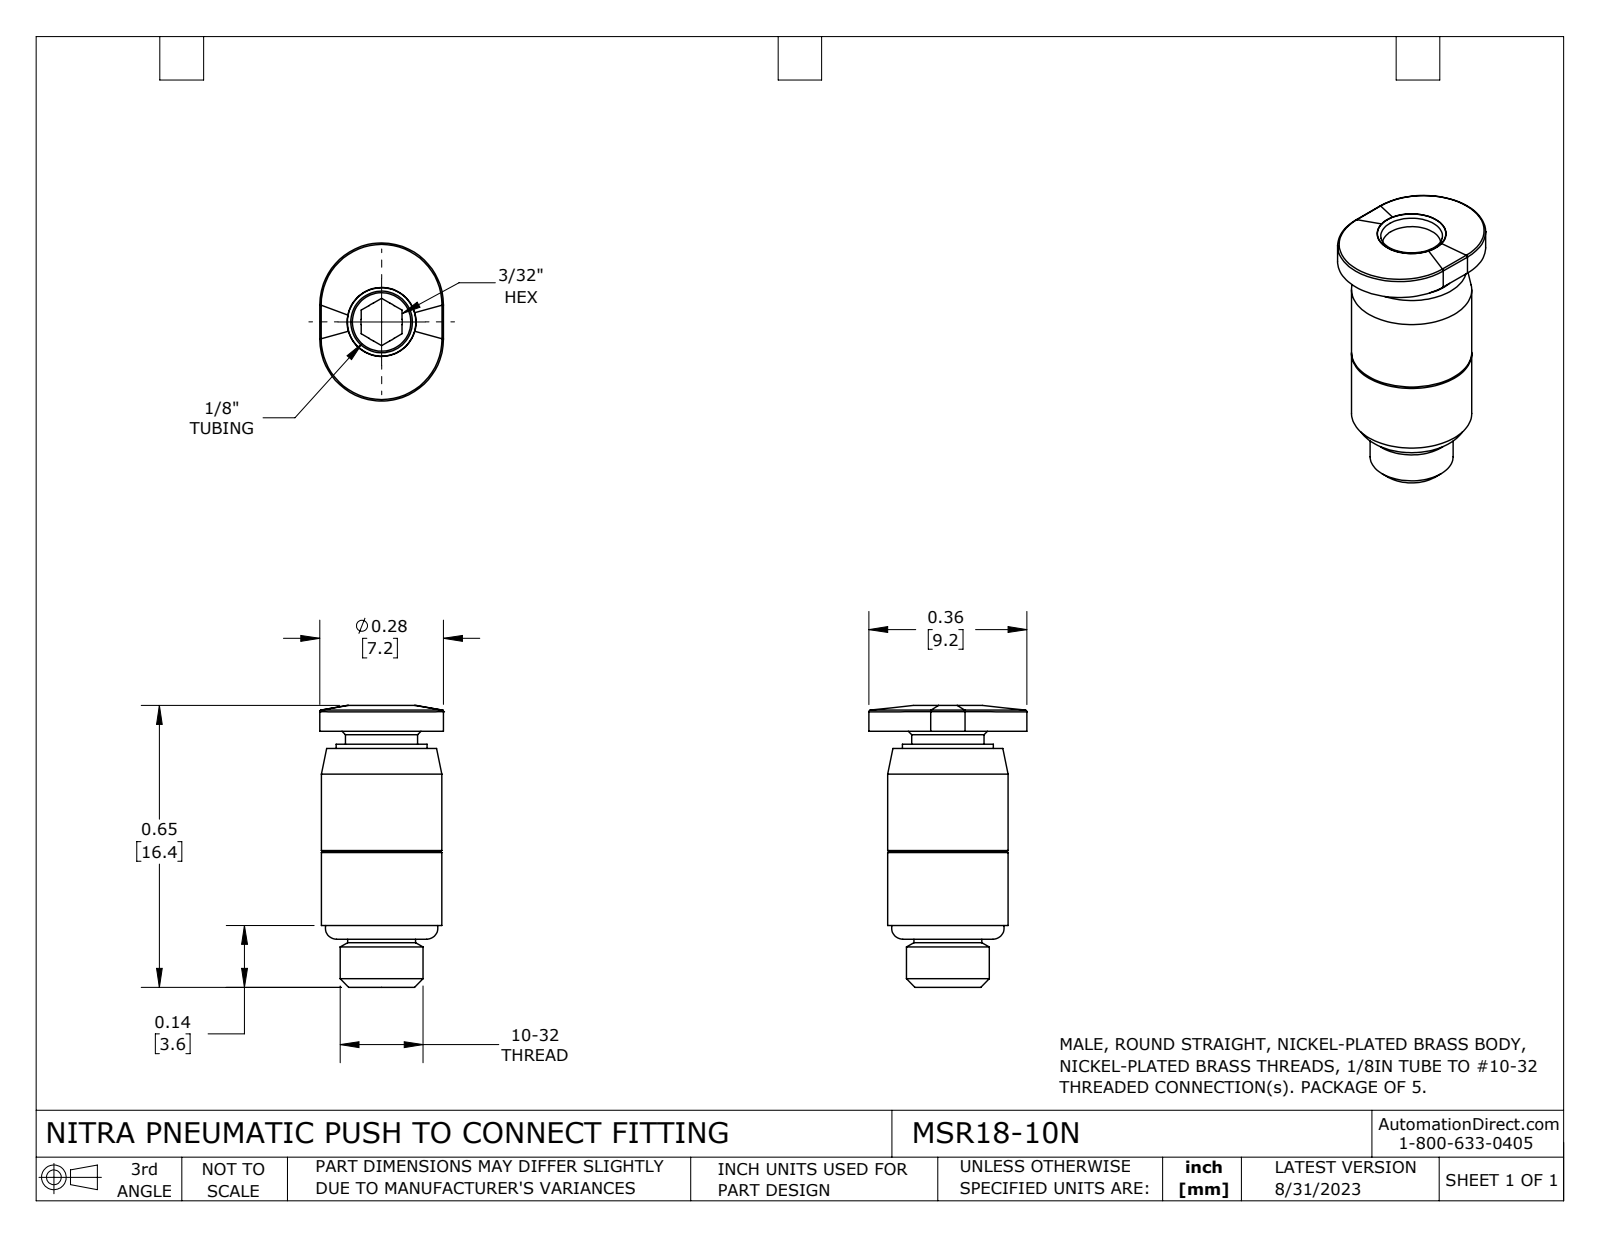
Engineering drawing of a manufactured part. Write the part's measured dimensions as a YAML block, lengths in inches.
part_name: "MSR18-10N"
step_written_by: "SolidWorks 2015 (CONFIG_CONTROL_DESIGN)"
units: inches
bodies: {solids: 2, faces: 68, planar: 11, cylindrical: 21, other: 36}
overall_size: [0.646, 0.362, 0.283]
volume: 0.026
surface_area: 1.107
round_holes:
  - {diameter: 0.094, count: 1}
  - {diameter: 0.134, count: 1}
round_bosses_or_shafts:
  - {diameter: 0.276, count: 1}
  - {diameter: 0.209, count: 1}
  - {diameter: 0.19, count: 1}
  - {diameter: 0.165, count: 1}
  - {diameter: 0.156, count: 1}
partial_cylinders:
  - {radius: 0.142, count: 2}
face_to_face_distances: [0.425, 0.039, 0.386, 0.396, 0.03, 0.161, 0.547, 0.557, 0.587, 0.201]
